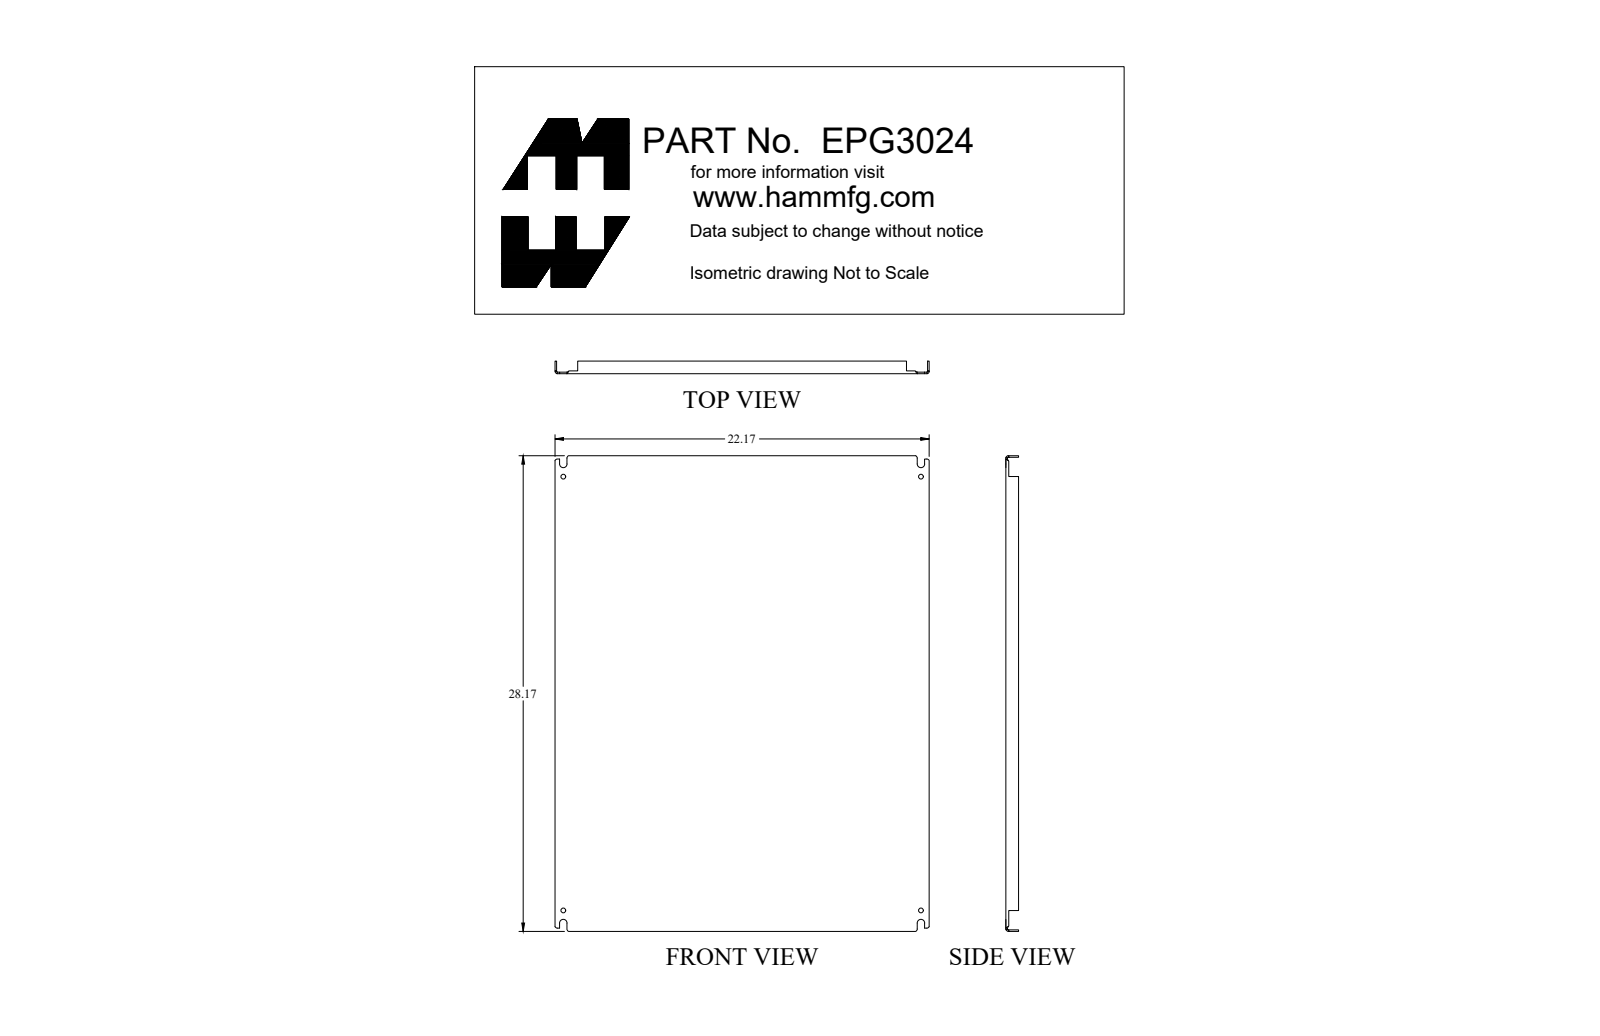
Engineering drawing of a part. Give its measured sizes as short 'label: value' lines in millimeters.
name: EPG3024
written by: SolidWorks 2018 (AUTOMOTIVE_DESIGN)
unit: mm
bodies: 1 solid, 128 faces (74 planar, 38 cylindrical, 16 other)
size: 715.5 × 563.1 × 19.1
volume: 1 056 000 mm³; area: 881 900 mm²
holes: 4× ⌀7.1
rounds: 4× R1.2, 4× R1.6, 4× R3.6, 4× R5.6
face distances: 2.4, 560.7, 713.1, 563.1, 558.3, 710.7, 715.5, 19.1, 16.6, 4.3
hole spacings: 538.2, 652.5, 845.8
